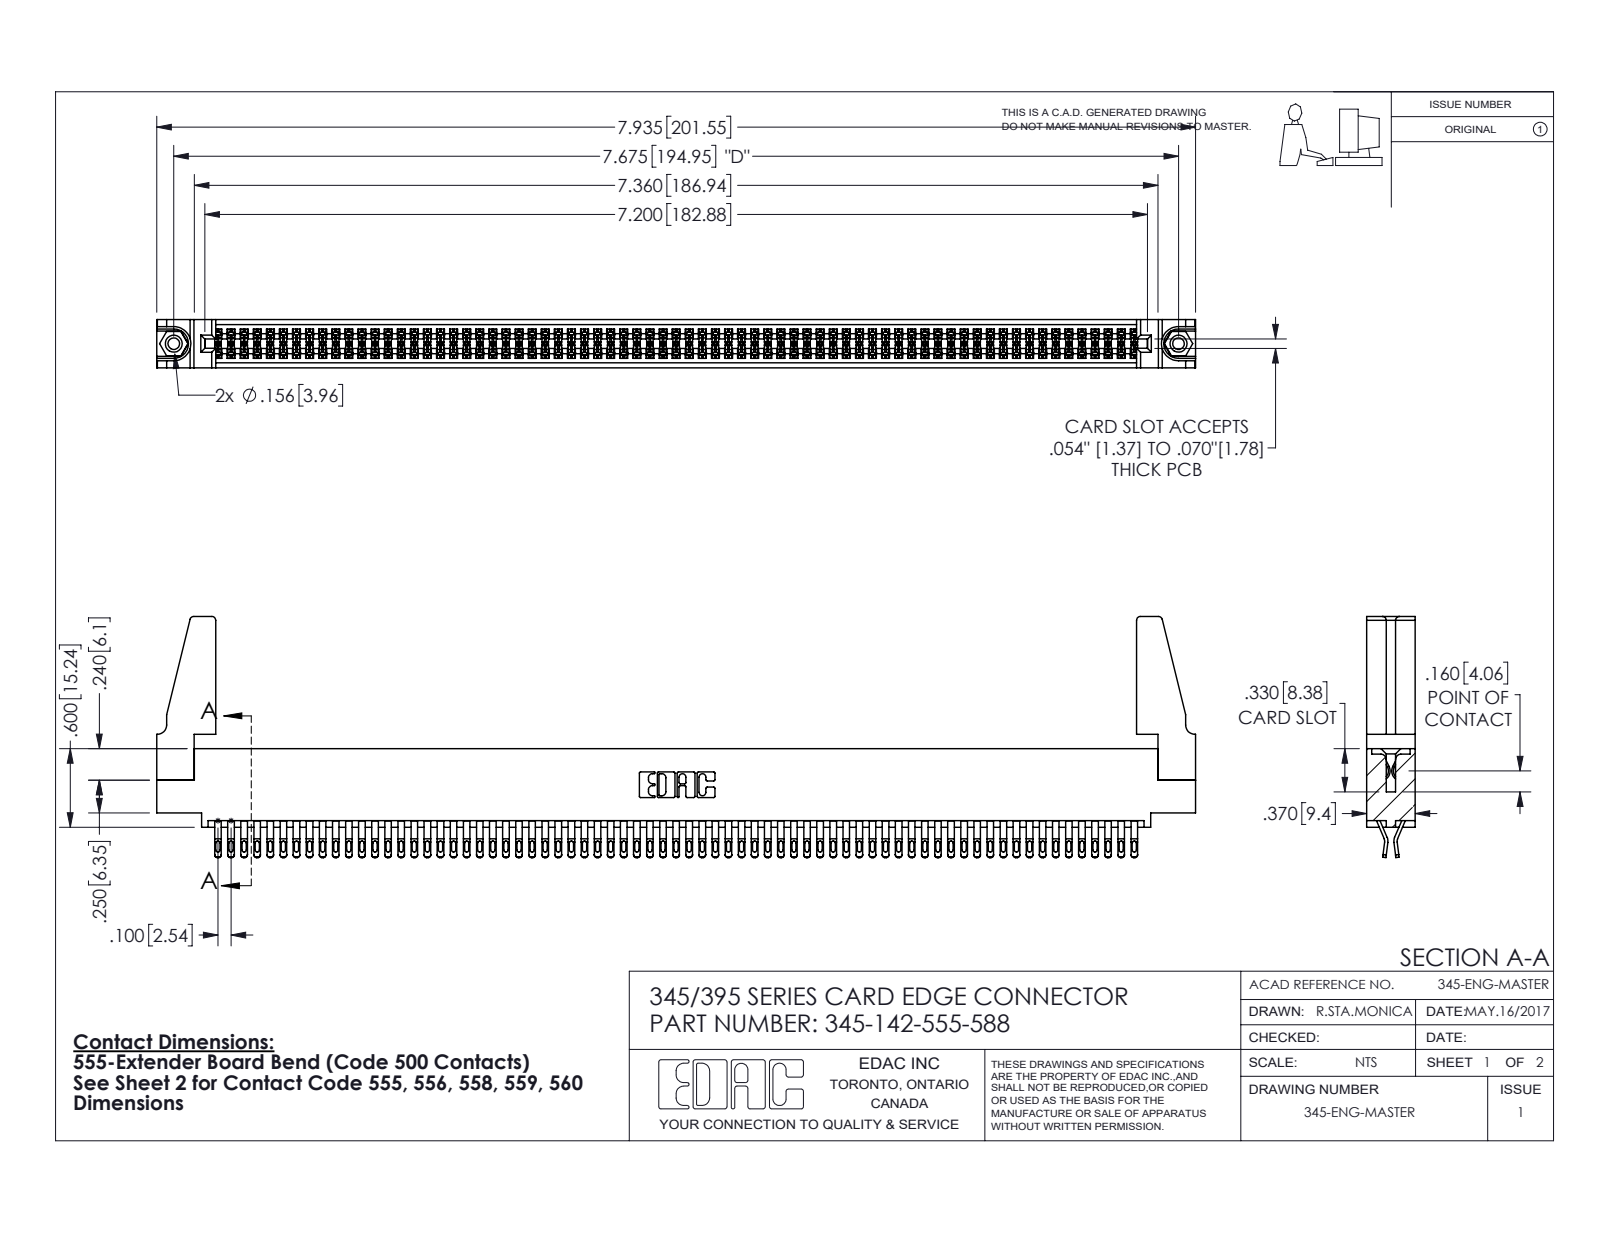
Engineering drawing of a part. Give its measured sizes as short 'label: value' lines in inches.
name: 345-250-001_345-250-001-102; 345-142-555-588; 345-220-078_345-220-088; 345-292-001_555 Tail (+1 more)
written by: SolidWorks 2016 (CONFIG_CONTROL_DESIGN)
unit: in
bodies: 147 solids, 8206 faces (4558 planar, 3632 cylindrical, 16 other)
size: 7.936 × 1.842 × 0.37
volume: 1.43 in³; area: 54.33 in²
holes: 2× ⌀0.089, 2× ⌀0.125, 2× ⌀0.156, 1× ⌀0.064
bosses: 2× ⌀0.155
rounds: 355× R0.016, 284× R0.02, 213× R0.006, 22× R0.01, 8× R0.03, 6× R0.007, 6× R0.031, 3× R0.026
face distances: 0.072, 0.298, 0.37, 0.025, 0.098, 0.272, 0.2, 0.225, 0.175, 0.149
hole spacings: 0.27, 7.439, 7.675
